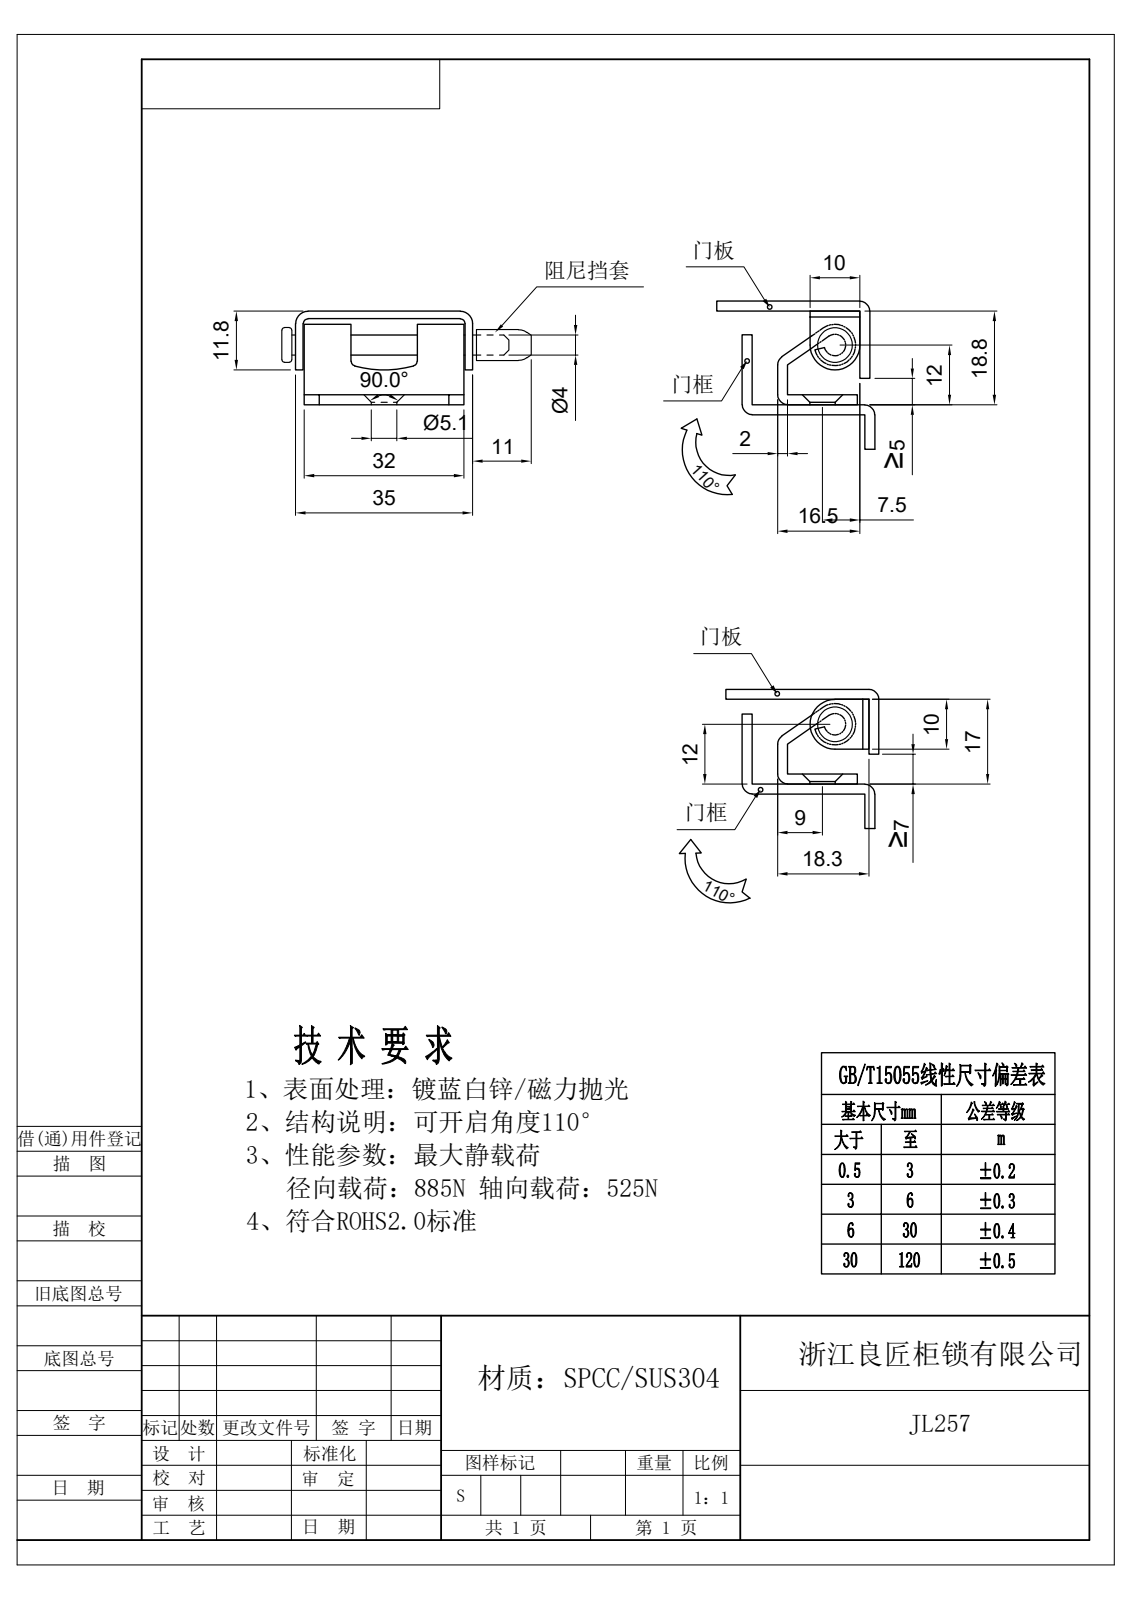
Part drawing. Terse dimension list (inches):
written by: Rhino 8.5 (CONFIG_CONTROL_DESIGN)
unit: in
bodies: 4 solids, 75 faces (33 planar, 27 cylindrical, 15 other)
size: 1.969 × 0.787 × 0.65
volume: 0.25 in³; area: 7.857 in²
holes: 1× ⌀0.157, 1× ⌀0.169, 1× ⌀0.17, 1× ⌀0.201
bosses: 1× ⌀0.276, 1× ⌀0.244
rounds: 2× R0.039, 2× R0.079, 2× R0.098, 1× R0.175, 1× R0.197
face distances: 0.079, 0.059, 0.65, 0.728, 0.787, 0.709, 0.091, 1.27, 0.069, 1.329
